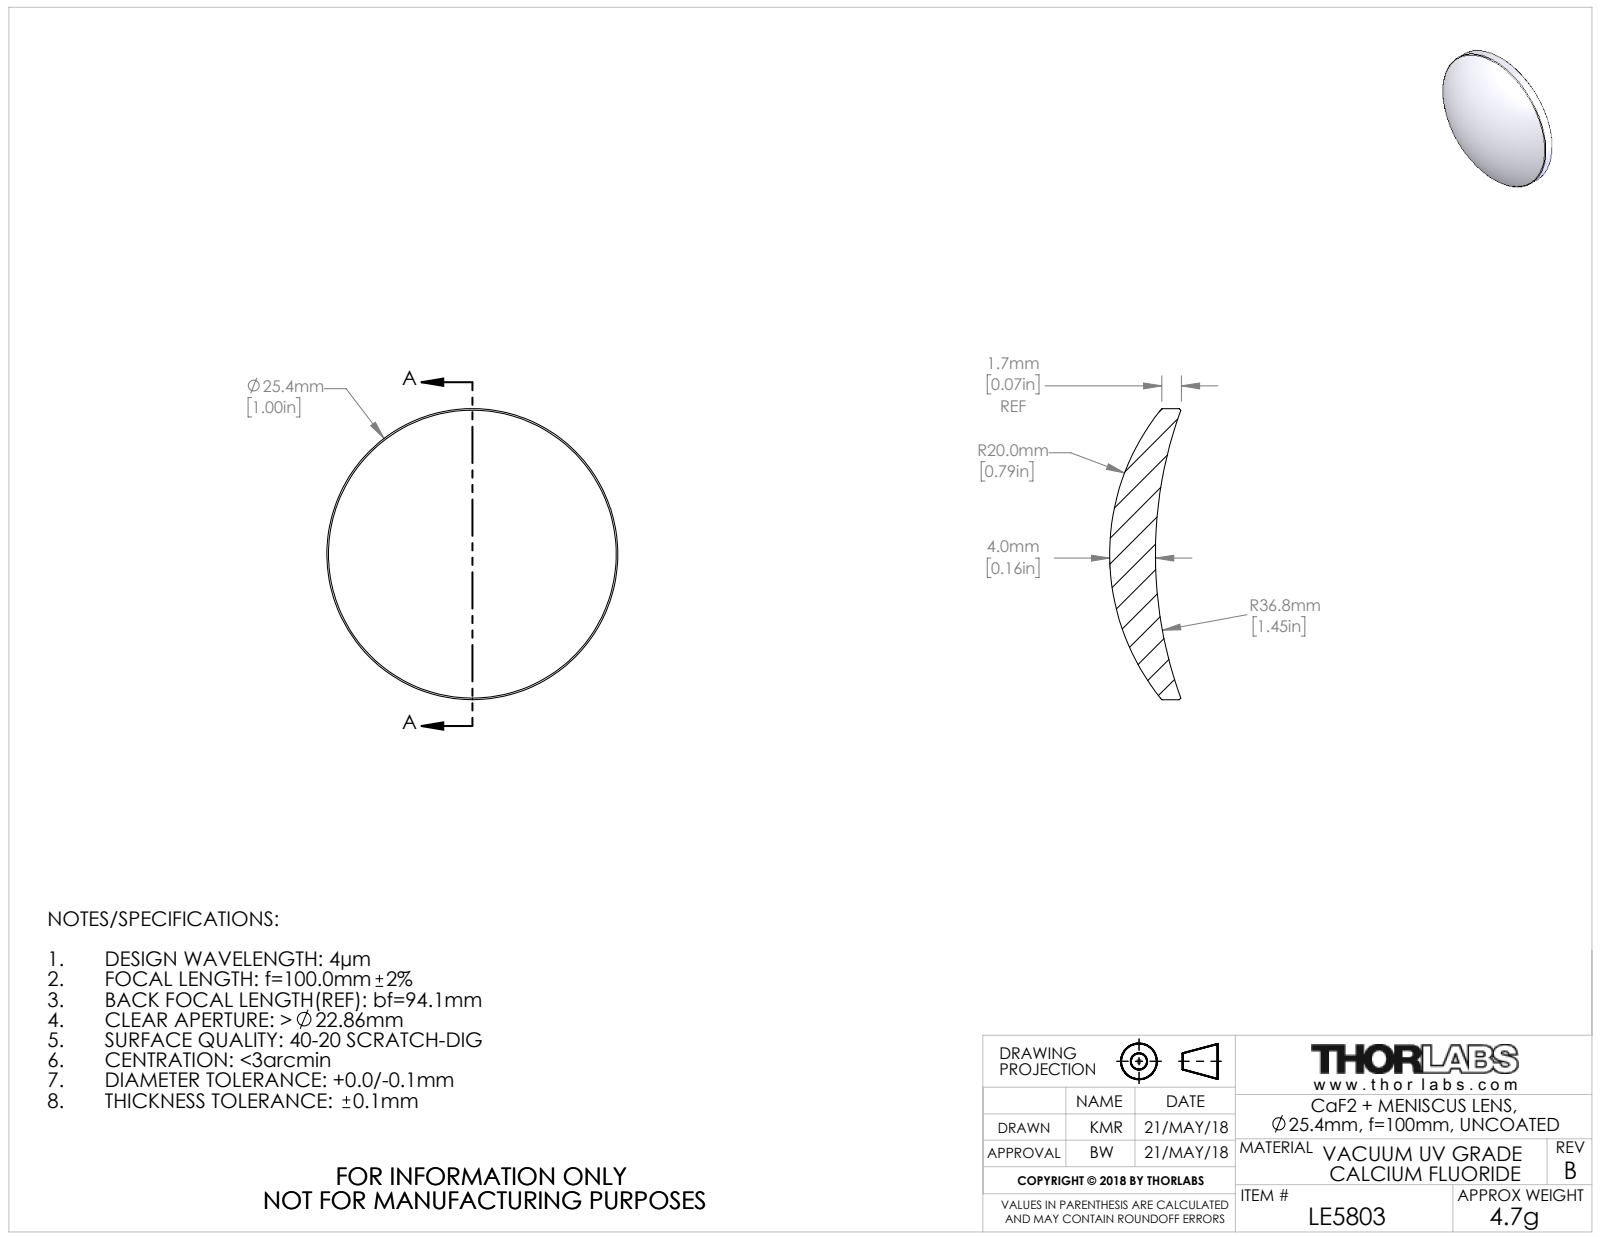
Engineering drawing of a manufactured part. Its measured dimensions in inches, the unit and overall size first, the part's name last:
Units: inches
Overall size (bounding box): 1 × 1 × 0.244
Round bosses / shafts (diameter × count): ⌀1 ×1
Volume: 0.091 in³ · Surface area: 1.889 in²
Bodies: 1 solid, 10 faces (0 planar, 2 cylindrical, 8 other)
Part name (STEP PRODUCT): 21989-E0W
STEP written by: SolidWorks 2016 (CONFIG_CONTROL_DESIGN)
